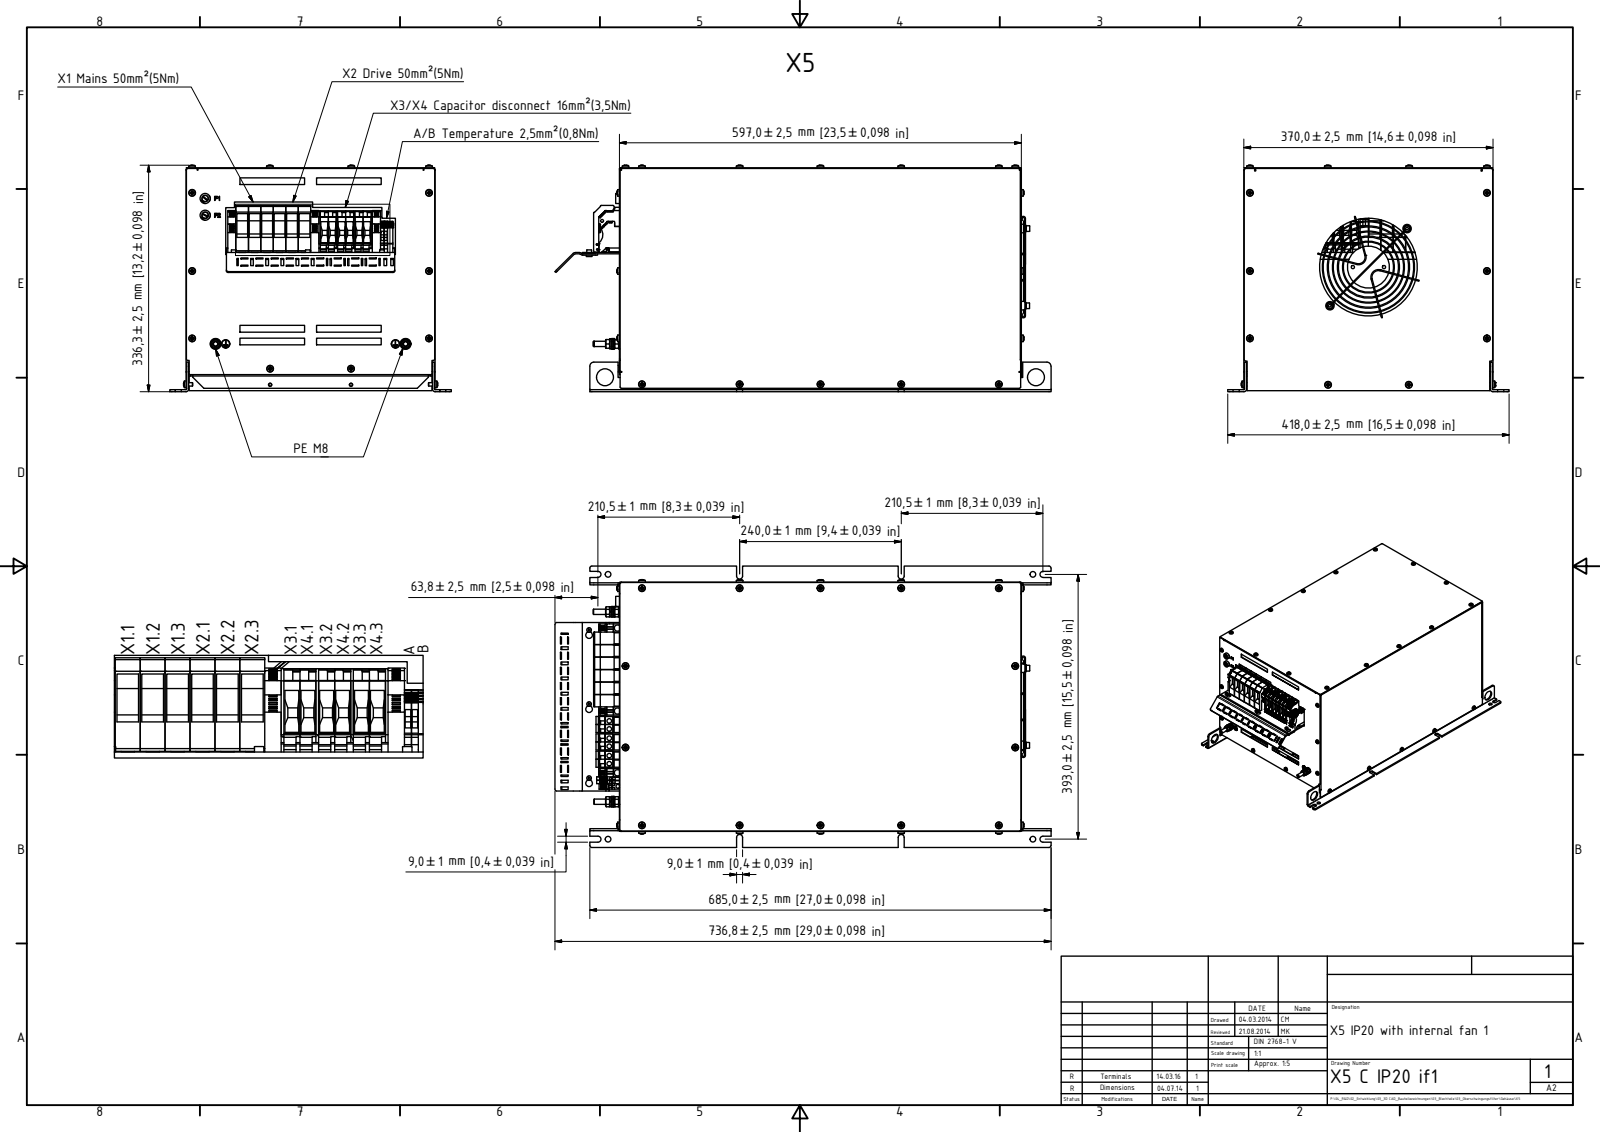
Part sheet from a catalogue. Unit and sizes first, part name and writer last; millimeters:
Units: millimetres
Overall size (bounding box): 736.77 × 418 × 336.32
Round holes (diameter × count): ⌀4.13 ×29, ⌀6.5 ×27, ⌀6.8 ×14, ⌀6 ×11, ⌀7 ×11, ⌀9 ×8, ⌀3.24 ×7, ⌀8.5 ×6, ⌀4 ×5, ⌀8.2 ×4, ⌀3.95 ×3, ⌀9.4 ×3
Round bosses / shafts (diameter × count): ⌀5 ×31, ⌀4.6 ×29, ⌀1.4 ×8, ⌀8.5 ×5, ⌀16 ×4, ⌀11.4 ×4, ⌀9.2 ×4, ⌀7 ×3
Partial cylindrical surfaces — rounded edges, fillets, slot ends (radius × count): R0.23 ×112, R0.5 ×76, R1 ×70, R0.15 ×56, R2 ×53, R0.1 ×41, R0.1 ×37, R0.2 ×29
Main face-to-face distances: 1, 369, 3, 368, 370, 309, 308, 306, 305, 596
Hole centre spacings: 120, 21, 352, 36.37, 145, 265, 385, 54.5
Volume: 2 495 000 mm³ · Surface area: 2 769 000 mm²
Bodies: 111 solids, 8073 faces (4720 planar, 2040 cylindrical, 1313 other)
Part name (STEP PRODUCT): 10100398 Deckel X5_X6; 10100399 Seitenwand X5; 10100396 Anschlussblech X5; 10100397 Lüfterblech X5 (+8 more)
STEP written by: Autodesk Inventor 2015 (AUTOMOTIVE_DESIGN)
